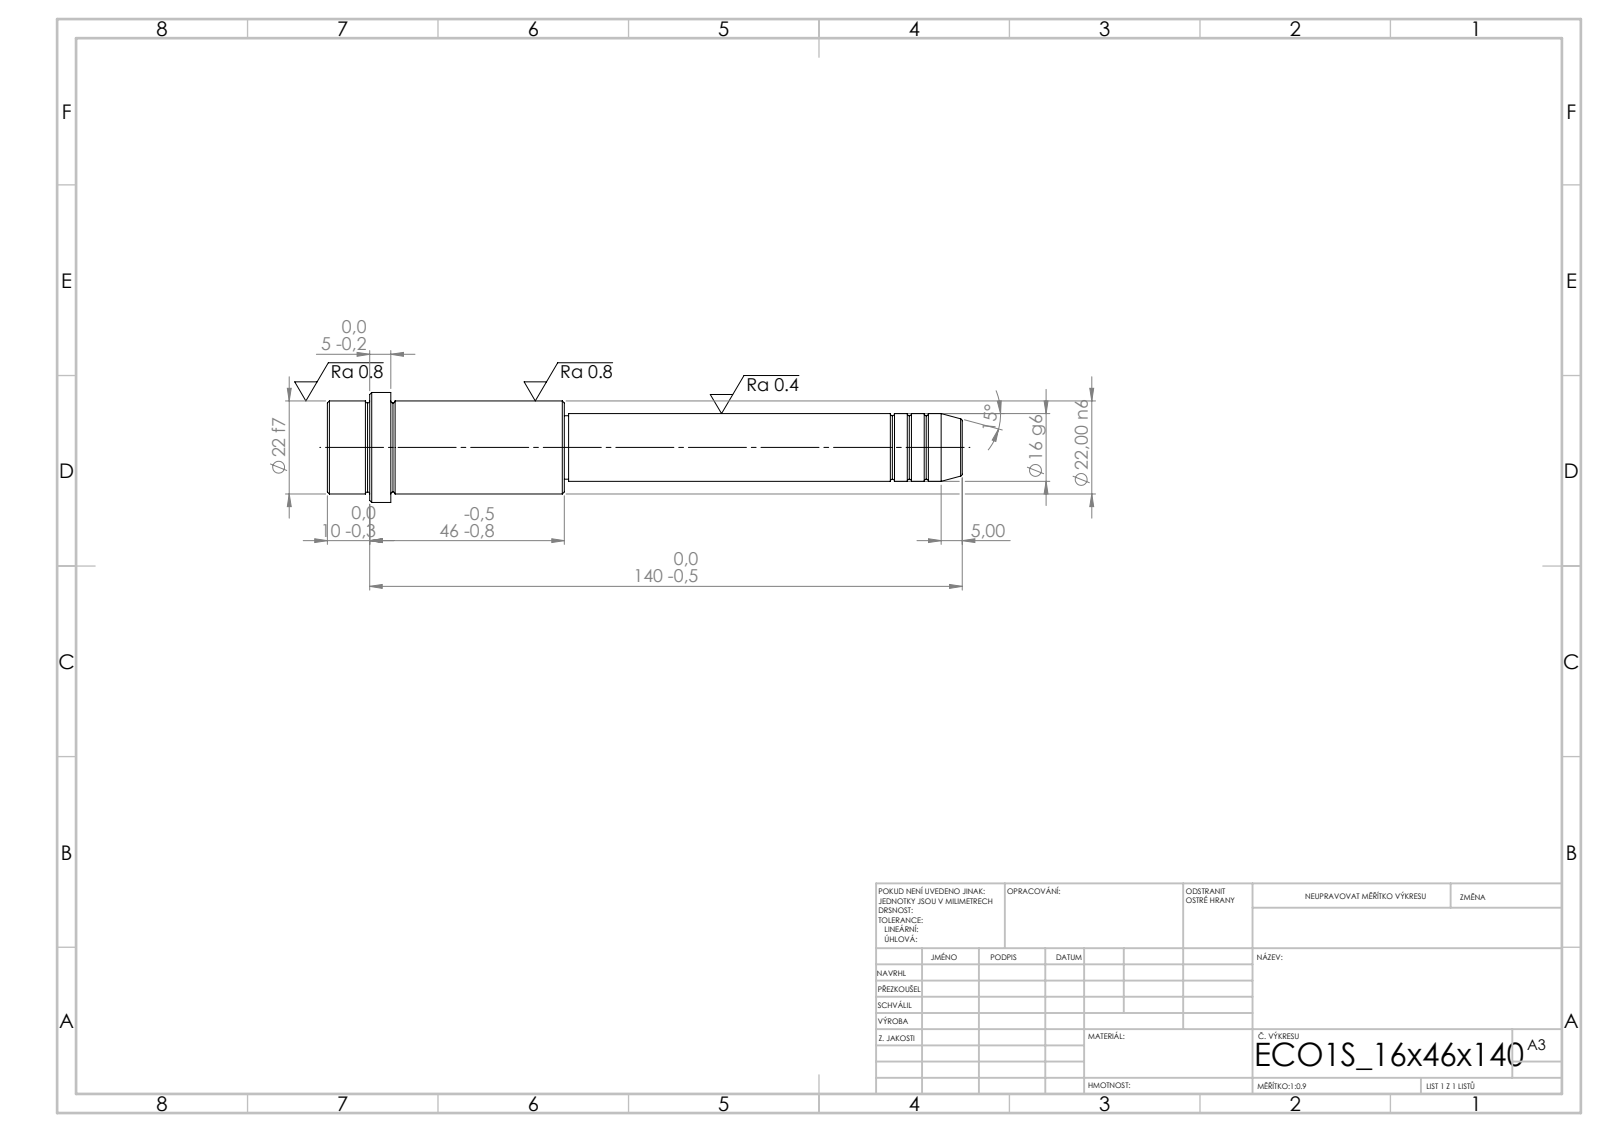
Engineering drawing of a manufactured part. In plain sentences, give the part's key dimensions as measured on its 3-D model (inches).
Its 3-D file was written by "SolidWorks 2019 (CONFIG_CONTROL_DESIGN)". It is 1 solid with 52 faces: 6 planar, 16 cylindrical and 30 other. Overall it measures 5.906 by 1.024 by 1.024 inches. Its volume is 2.479 cubic inches and its surface area 15.14 square inches. Round bosses or shafts: 1 of diameter 1.024, 1 of diameter 0.866, 1 of diameter 0.63, 1 of diameter 0.591. The main face-to-face distances are 2.205, 1.614, 0.591, 3.701, 5.315, 5.906, 5.512, 1.811, 0.197, 0.394.
